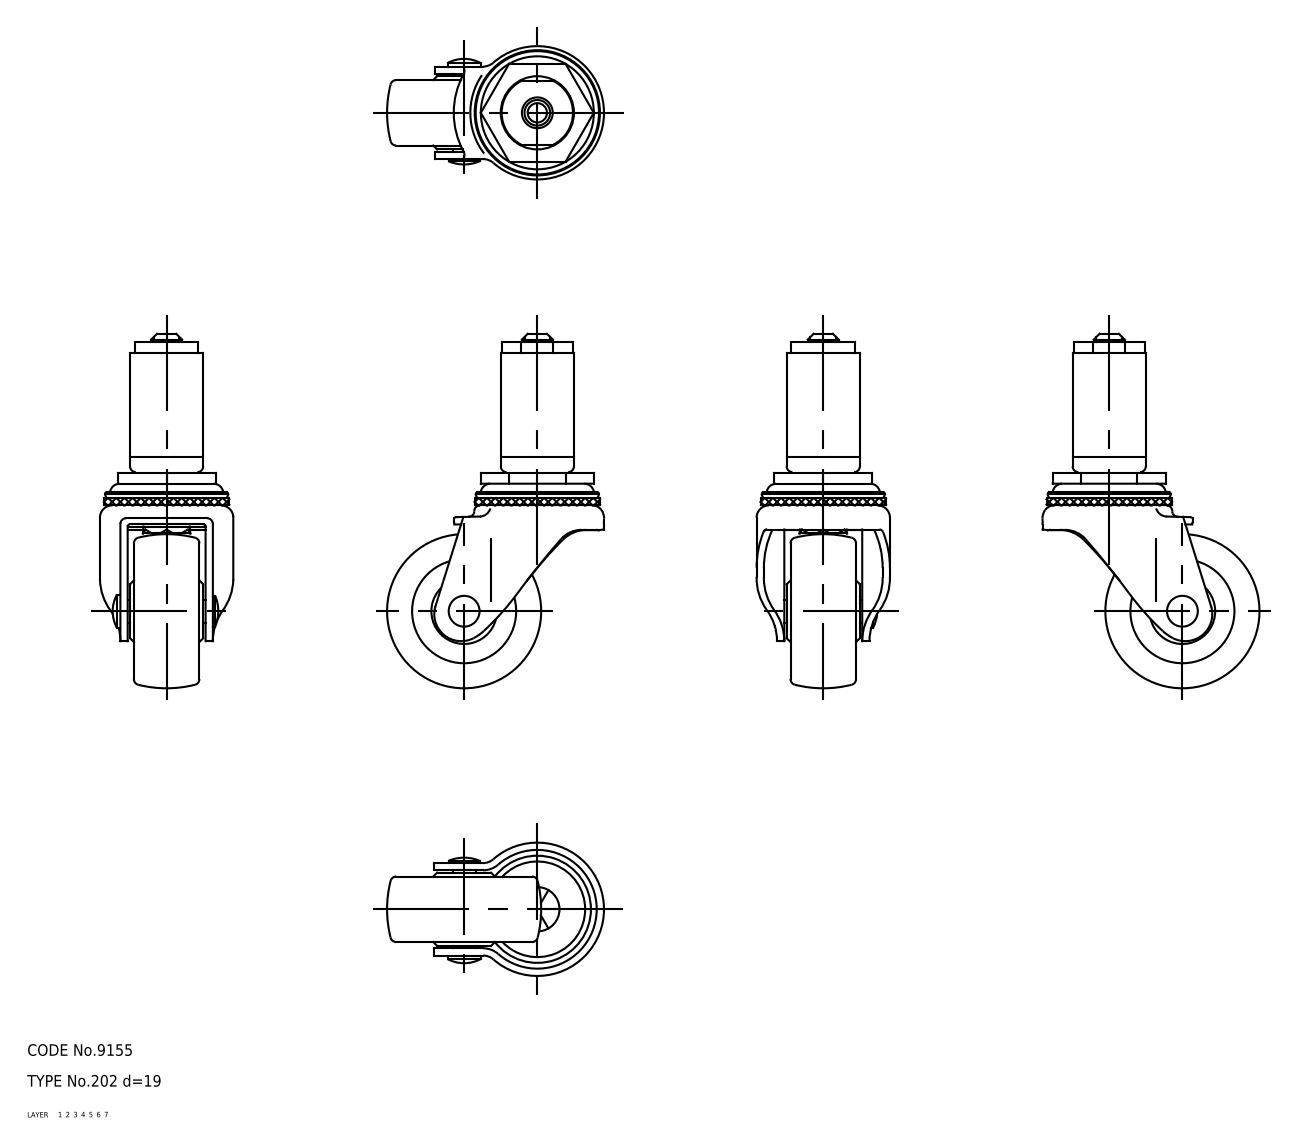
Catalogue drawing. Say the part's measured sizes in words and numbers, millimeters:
The part is named "wheel; main shaft; axle; No_202_d19_21092_36". Its 3-D file was written by "CADfix (AUTOMOTIVE_DESIGN)". It is 4 solids with 179 faces: 0 planar, 0 cylindrical and 179 other. Overall it measures 92 by 56.3 by 34.6 millimeters. Its volume is 42 732 cubic millimeters and its surface area 16 490 square millimeters.
